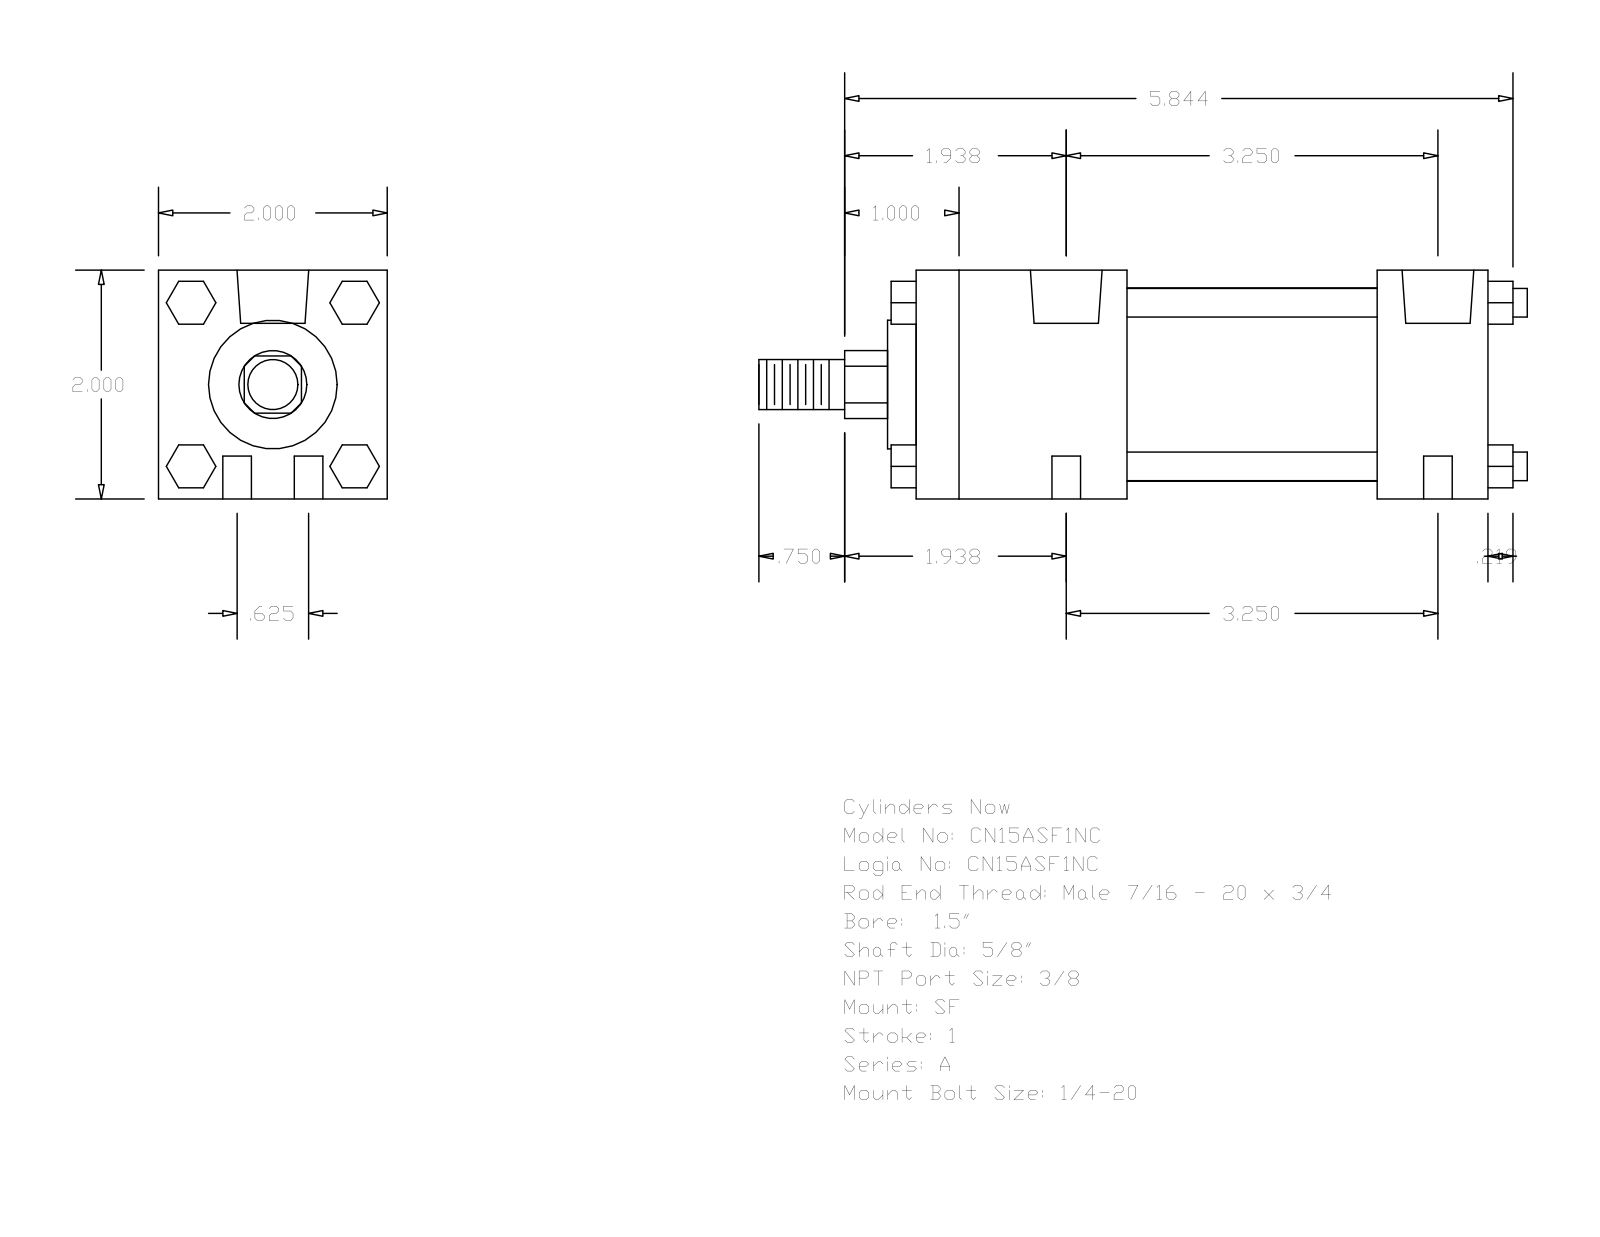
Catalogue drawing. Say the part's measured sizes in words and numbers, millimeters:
The part is named "A_SF__0150_0.625". Its 3-D file was written by "GSSL Pune (CONFIG_CONTROL_DESIGN)". It is 0 solids with 124 faces: 94 planar, 30 cylindrical and 0 other. Overall it measures 170.66 by 50.8 by 50.8 millimeters. Round holes: 4 of diameter 6.35, 2 of diameter 5.56, 2 of diameter 15.93. Round bosses or shafts: 4 of diameter 6.35, 1 of diameter 42.93, 1 of diameter 28.57, 1 of diameter 15.88, 1 of diameter 11.11. Partial cylindrical surfaces (rounded edges, fillets, slot ends): 1 of radius 7.54. The main face-to-face distances are 50.8, 127, 46.83, 102.39, 55.56, 80.17, 24.61, 6.35, 9.52, 53.18. The hole center spacings are 7.94, 82.93, 82.55, 15.88, 84.06, 74.61.
